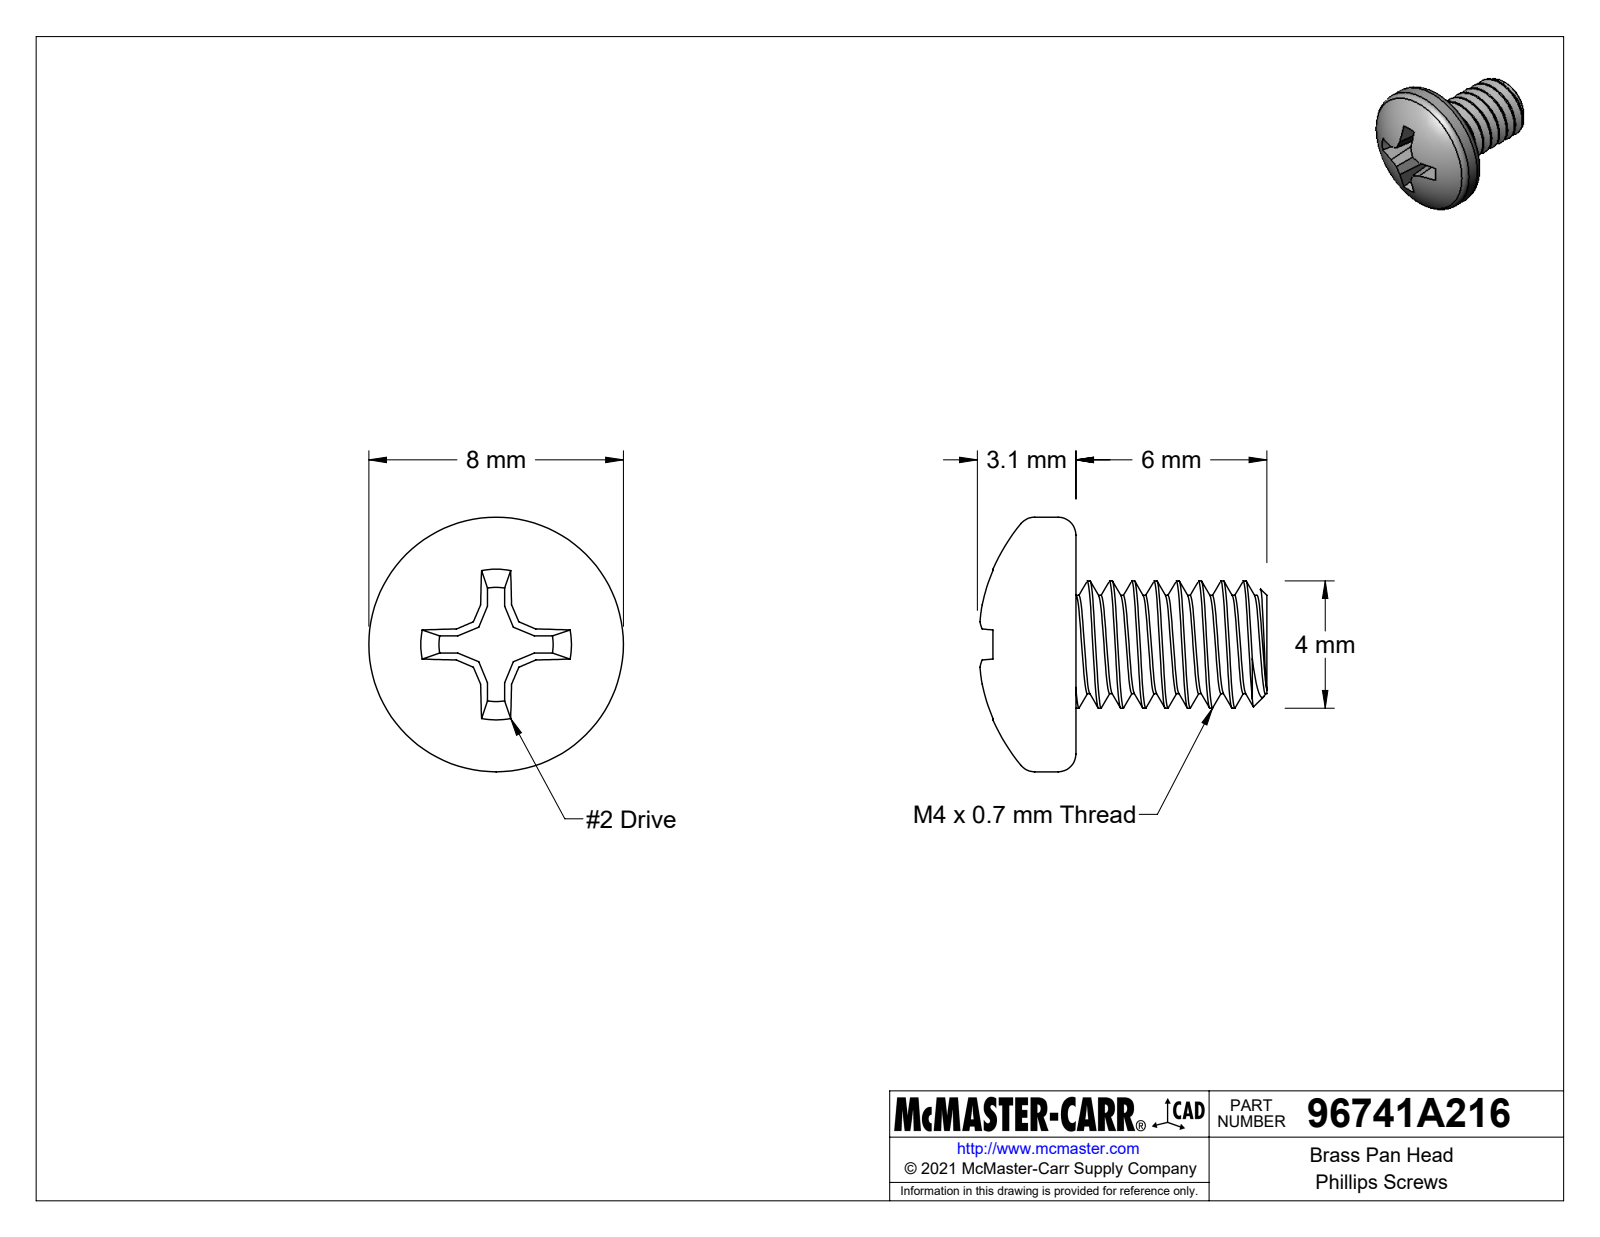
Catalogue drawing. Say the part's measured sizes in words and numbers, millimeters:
The part is named "96741A216_Brass Pan Head Phillips Screws". Its 3-D file was written by "SolidWorks 2017 (CONFIG_CONTROL_DESIGN)". It is 1 solid with 82 faces: 19 planar, 45 cylindrical and 18 other. Overall it measures 9.01 by 8 by 8 millimeters. Its volume is 160 cubic millimeters and its surface area 284 square millimeters. Round bosses or shafts: 1 of diameter 8, 1 of diameter 4, 1 of diameter 3.09. The main face-to-face distances are 6, 6.47, 0.47.
